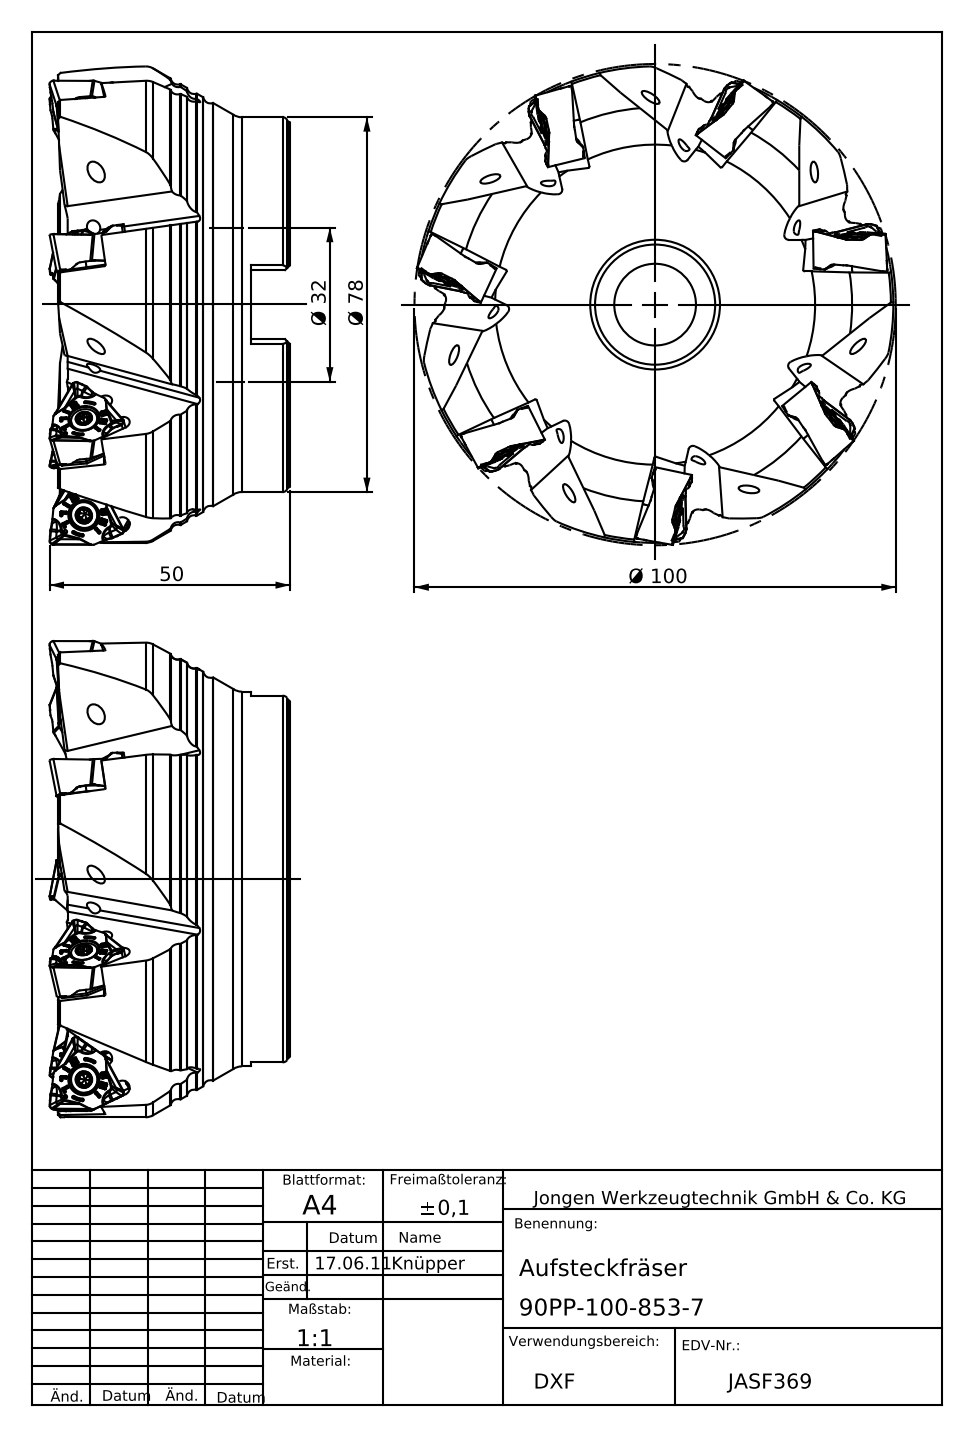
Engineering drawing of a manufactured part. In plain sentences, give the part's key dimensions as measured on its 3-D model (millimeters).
The part is named "90PP-100-853-7". Its 3-D file was written by "SolidWorks 2010 (AUTOMOTIVE_DESIGN)". It is 1 solid with 455 faces: 122 planar, 134 cylindrical and 199 other. Overall it measures 100 by 100 by 50 millimeters. Its volume is 259 698 cubic millimeters and its surface area 39 457 square millimeters. Round holes: 7 of diameter 3, 1 of diameter 17, 1 of diameter 25, 1 of diameter 32, 1 of diameter 32.15, 1 of diameter 32.3. Round bosses or shafts: 1 of diameter 100, 1 of diameter 99.15, 1 of diameter 78. Partial cylindrical surfaces (rounded edges, fillets, slot ends): 49 of radius 0.3, 14 of radius 1.5. The main face-to-face distances are 46.25, 48.2, 1.95, 8, 38.25, 40.2, 28, 20, 18.25, 20.2.
